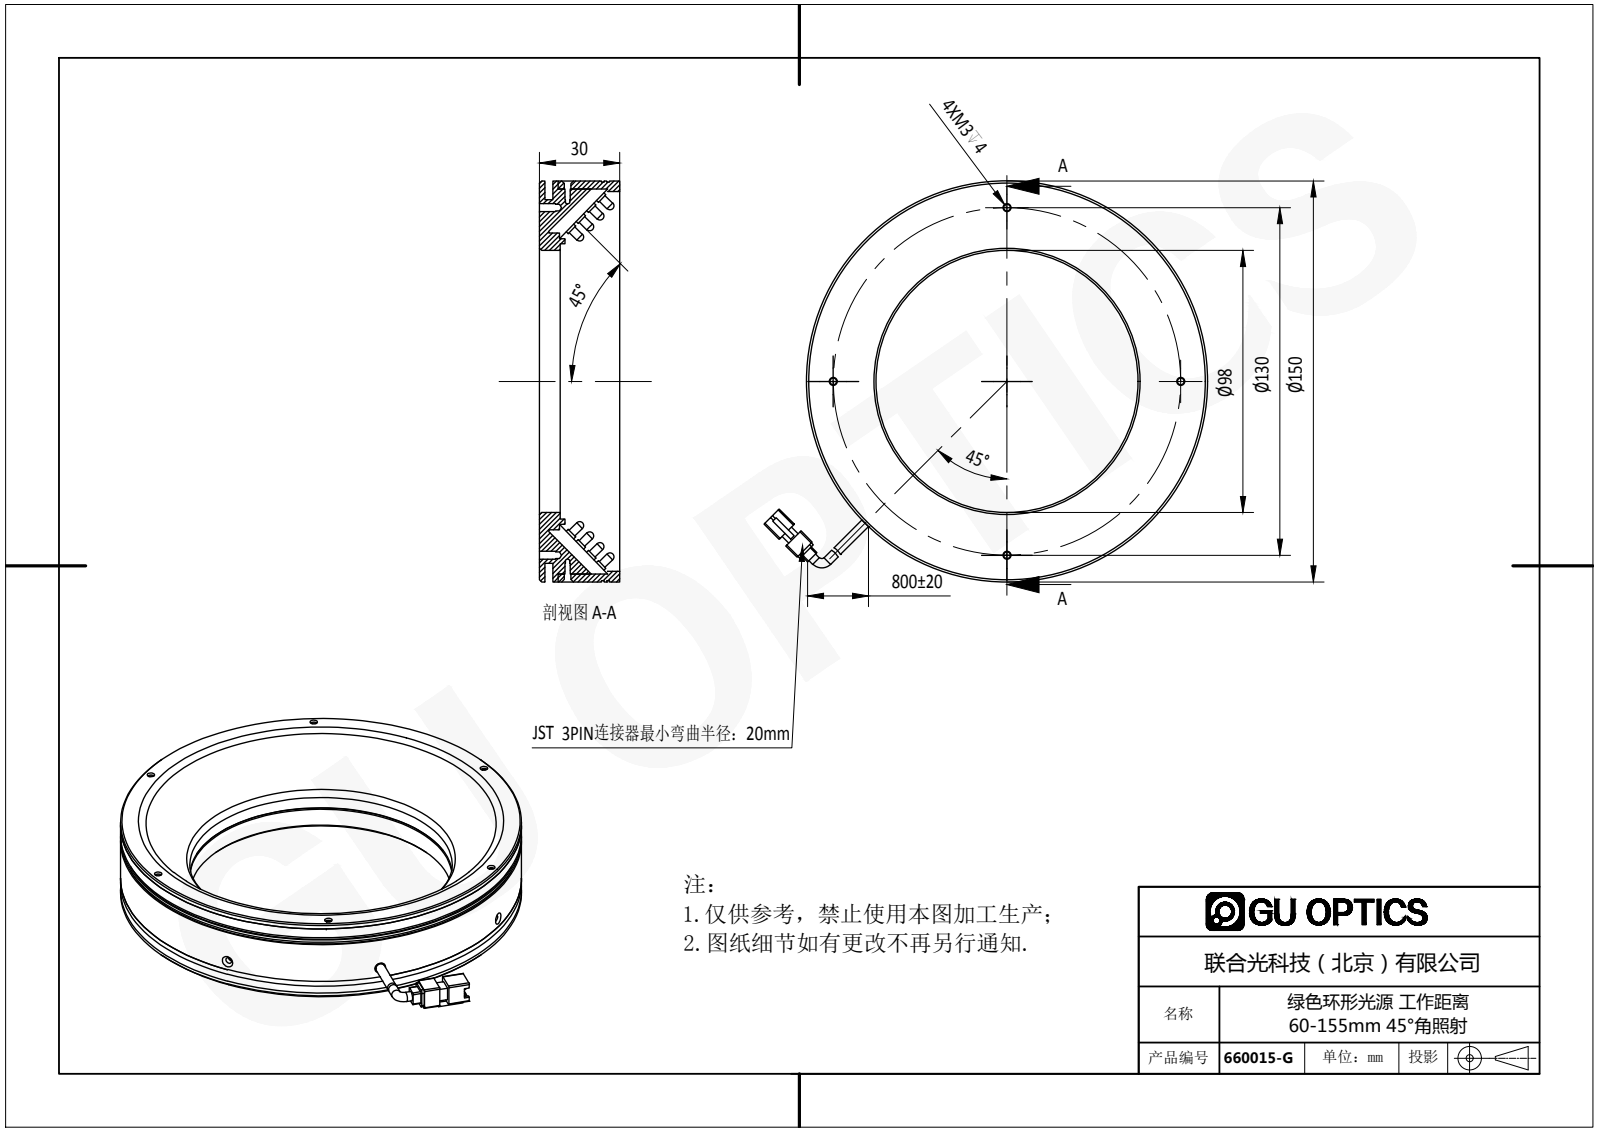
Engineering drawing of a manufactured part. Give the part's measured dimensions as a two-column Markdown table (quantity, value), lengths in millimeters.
| quantity | value |
| --- | --- |
| part name | 660015-G |
| STEP written by | SolidWorks 2016 (AUTOMOTIVE_DESIGN) |
| units | millimeters |
| bodies | 326 solids, 5782 faces (3937 planar, 1453 cylindrical, 392 other) |
| overall size | 165.86 × 150 × 32 |
| volume | 171 732 mm³ |
| surface area | 146 693 mm² |
| round holes (diameter × count) | 1.1 × 6, 1.4 × 6, 1.5 × 6, 2.8 × 6, 2.5 × 4, 3 × 4, 3.5 × 4, 1.6 × 2, 2 × 2, 2.4 × 2, 3.6 × 1, 98 × 1 |
| round bosses / shafts (diameter × count) | 3.8 × 320, 3 × 320, 3.5 × 2, 150 × 1, 149 × 1, 144 × 1, 136 × 1, 111 × 1 |
| partial cylindrical surfaces (radius × count) | 0.5 × 12, 1 × 4, 8 × 1 |
| main face-to-face distances | 2, 30, 5, 25, 3, 7, 28, 23, 0.5, 32 |
| hole center spacings | 72, 124.71, 18.79, 133.04, 36.1, 52.82, 55.11, 65 |
